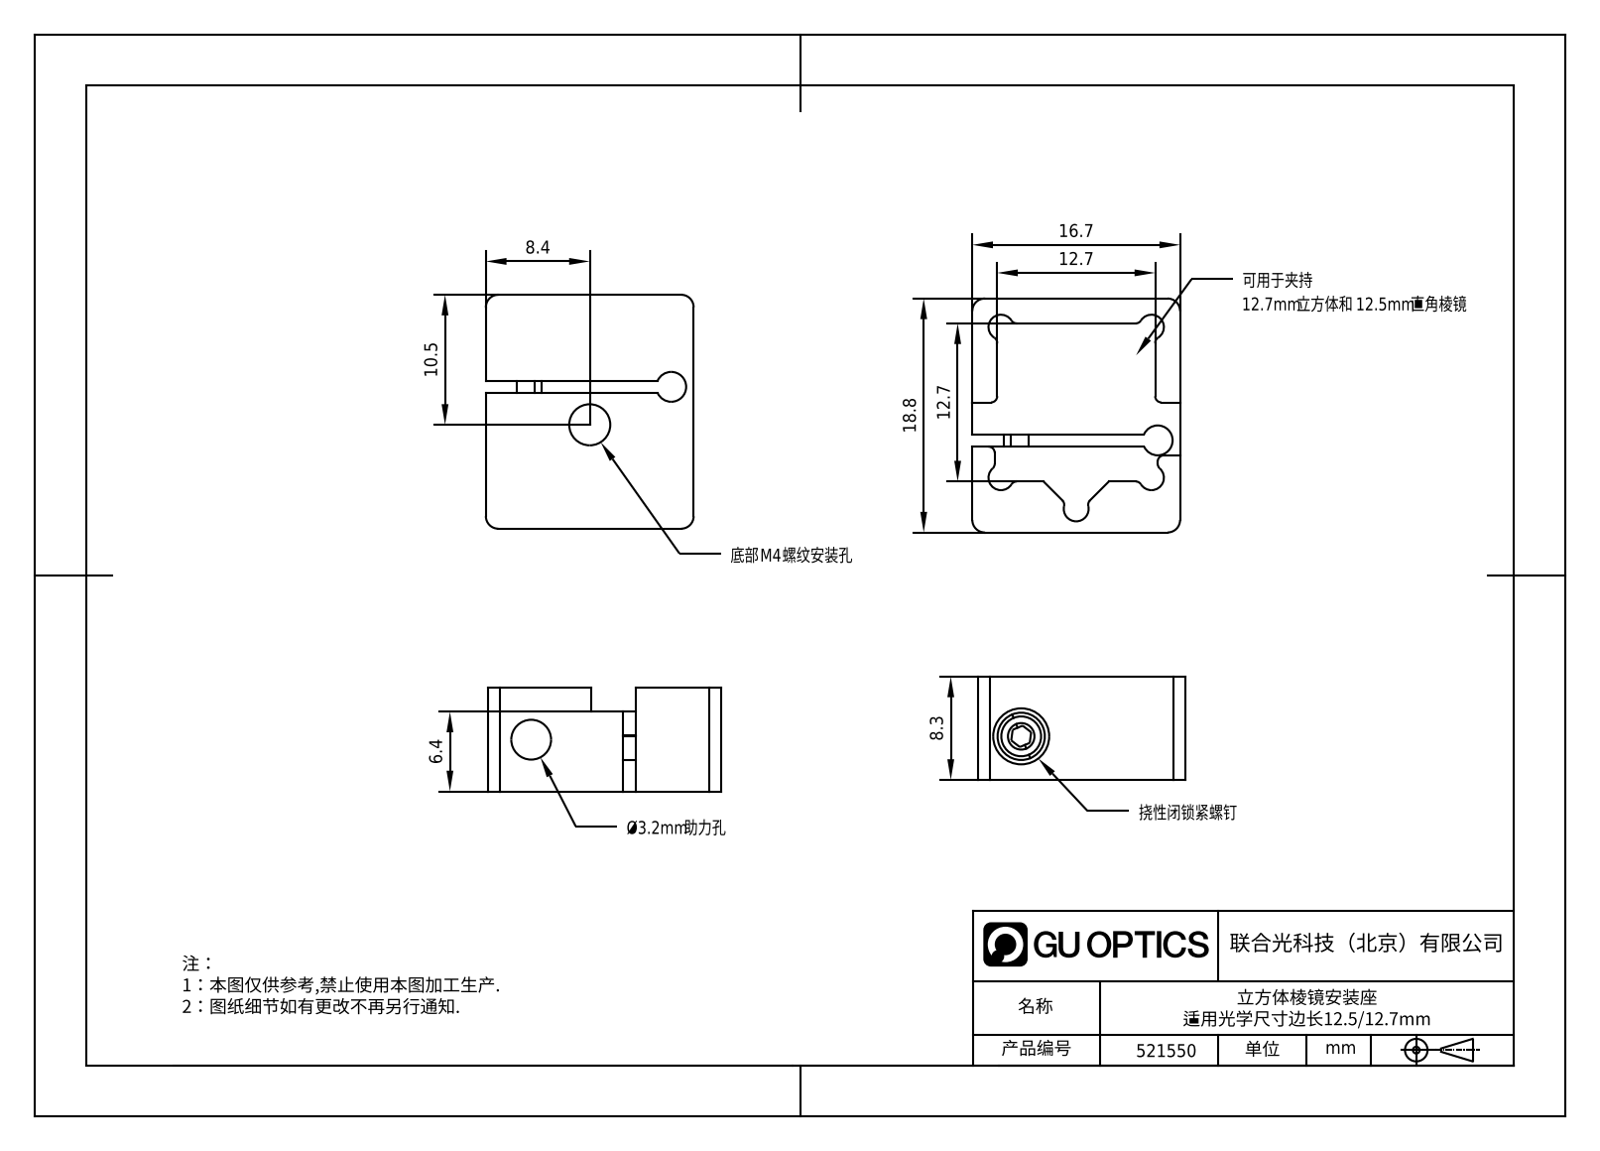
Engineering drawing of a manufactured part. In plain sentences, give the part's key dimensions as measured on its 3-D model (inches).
The part is named "1.3.13.1.1_平台安装座主体，用于0.5英寸分束立方和直角棱镜，M4螺孔; 1.3.13.1_ZZP-0.5_平台安装座，用于0.5英寸分束立方和直角棱镜，M4螺孔; 30.1.圆柱头内六角不锈钢螺丝_30.1.19-M2*8". Its 3-D file was written by "SolidWorks 2021 (CONFIG_CONTROL_DESIGN)". It is 2 solids with 88 faces: 35 planar, 43 cylindrical and 10 other. Overall it measures 0.74 by 0.657 by 0.327 inches. Its volume is 0.116 cubic inches and its surface area 2.897 square inches. Round holes: 2 of diameter 0.094, 1 of diameter 0.063, 1 of diameter 0.126, 1 of diameter 0.13, 1 of diameter 0.177. Round bosses or shafts: 1 of diameter 0.15, 1 of diameter 0.079. Partial cylindrical surfaces (rounded edges, fillets, slot ends): 14 of radius 0.02, 9 of radius 0.039. The main face-to-face distances are 0.252, 0.327, 0.075, 0.657, 0.74, 0.039, 0.429, 0.311, 0.469, 0.272. The hole center spacings are 0.285.
